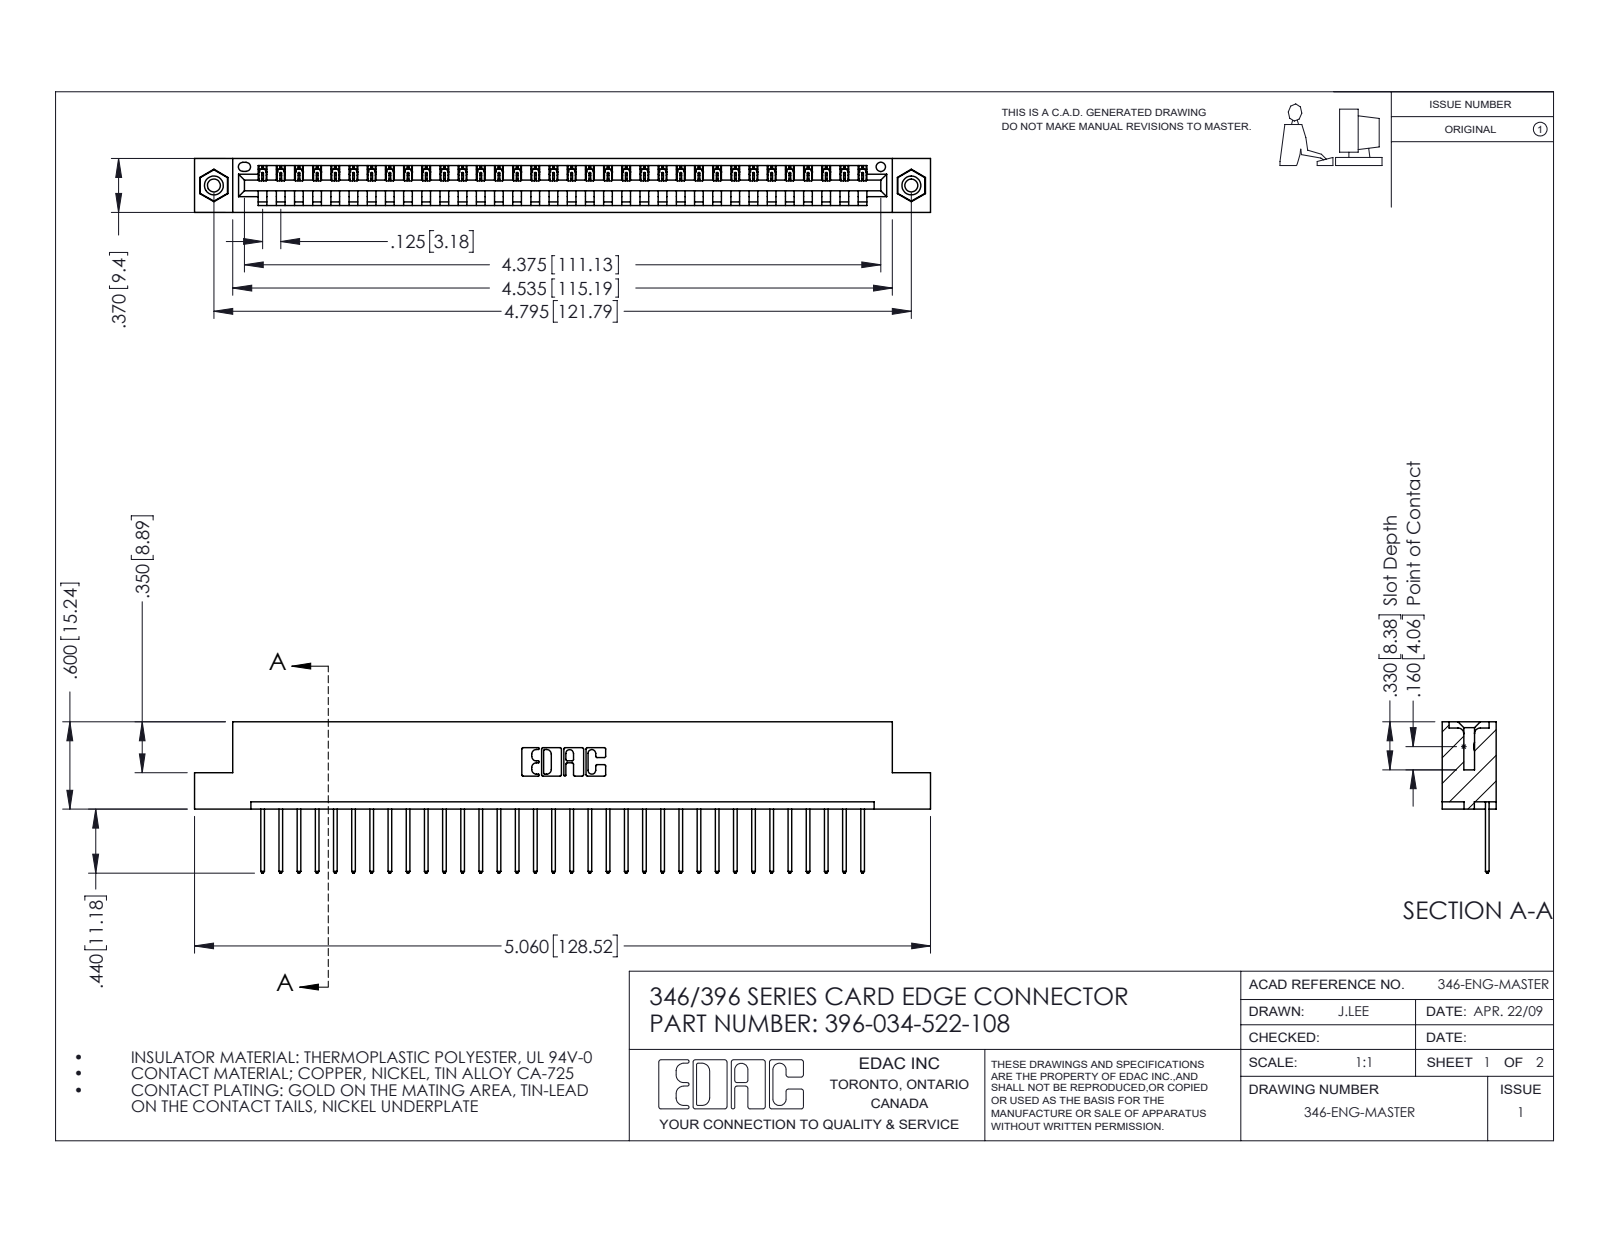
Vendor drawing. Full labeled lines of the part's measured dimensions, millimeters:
Part name (STEP PRODUCT): 345-250-001_345-250-003-102; 346 Part_Flush Mounting Lugs - 0.156 Dia-TI; 396-034-522-108; 345-292-001_345-293-122
STEP written by: SolidWorks 2016 (CONFIG_CONTROL_DESIGN)
Units: millimetres
Bodies: 37 solids, 2154 faces (1468 planar, 670 cylindrical, 16 other)
Overall size (bounding box): 128.5 × 26.4 × 9.4
Volume: 12 200 mm³ · Surface area: 15 370 mm²
Round holes (diameter × count): ⌀2.3 ×2, ⌀3.2 ×2, ⌀4 ×2, ⌀1.6 ×1
Round bosses / shafts (diameter × count): ⌀3.9 ×2
Partial cylindrical surfaces — rounded edges, fillets, slot ends (radius × count): R0.2 ×68, R0.3 ×68, R0.3 ×22, R0.2 ×6, R0.8 ×6, R0.7 ×3, R0.8 ×2, R1 ×2
Main face-to-face distances: 1.2, 8.2, 9.4, 6.4, 1.8, 7.6, 0.6, 3.8, 5.6, 2.5
Hole centre spacings: 6.2, 116.5, 121.8
